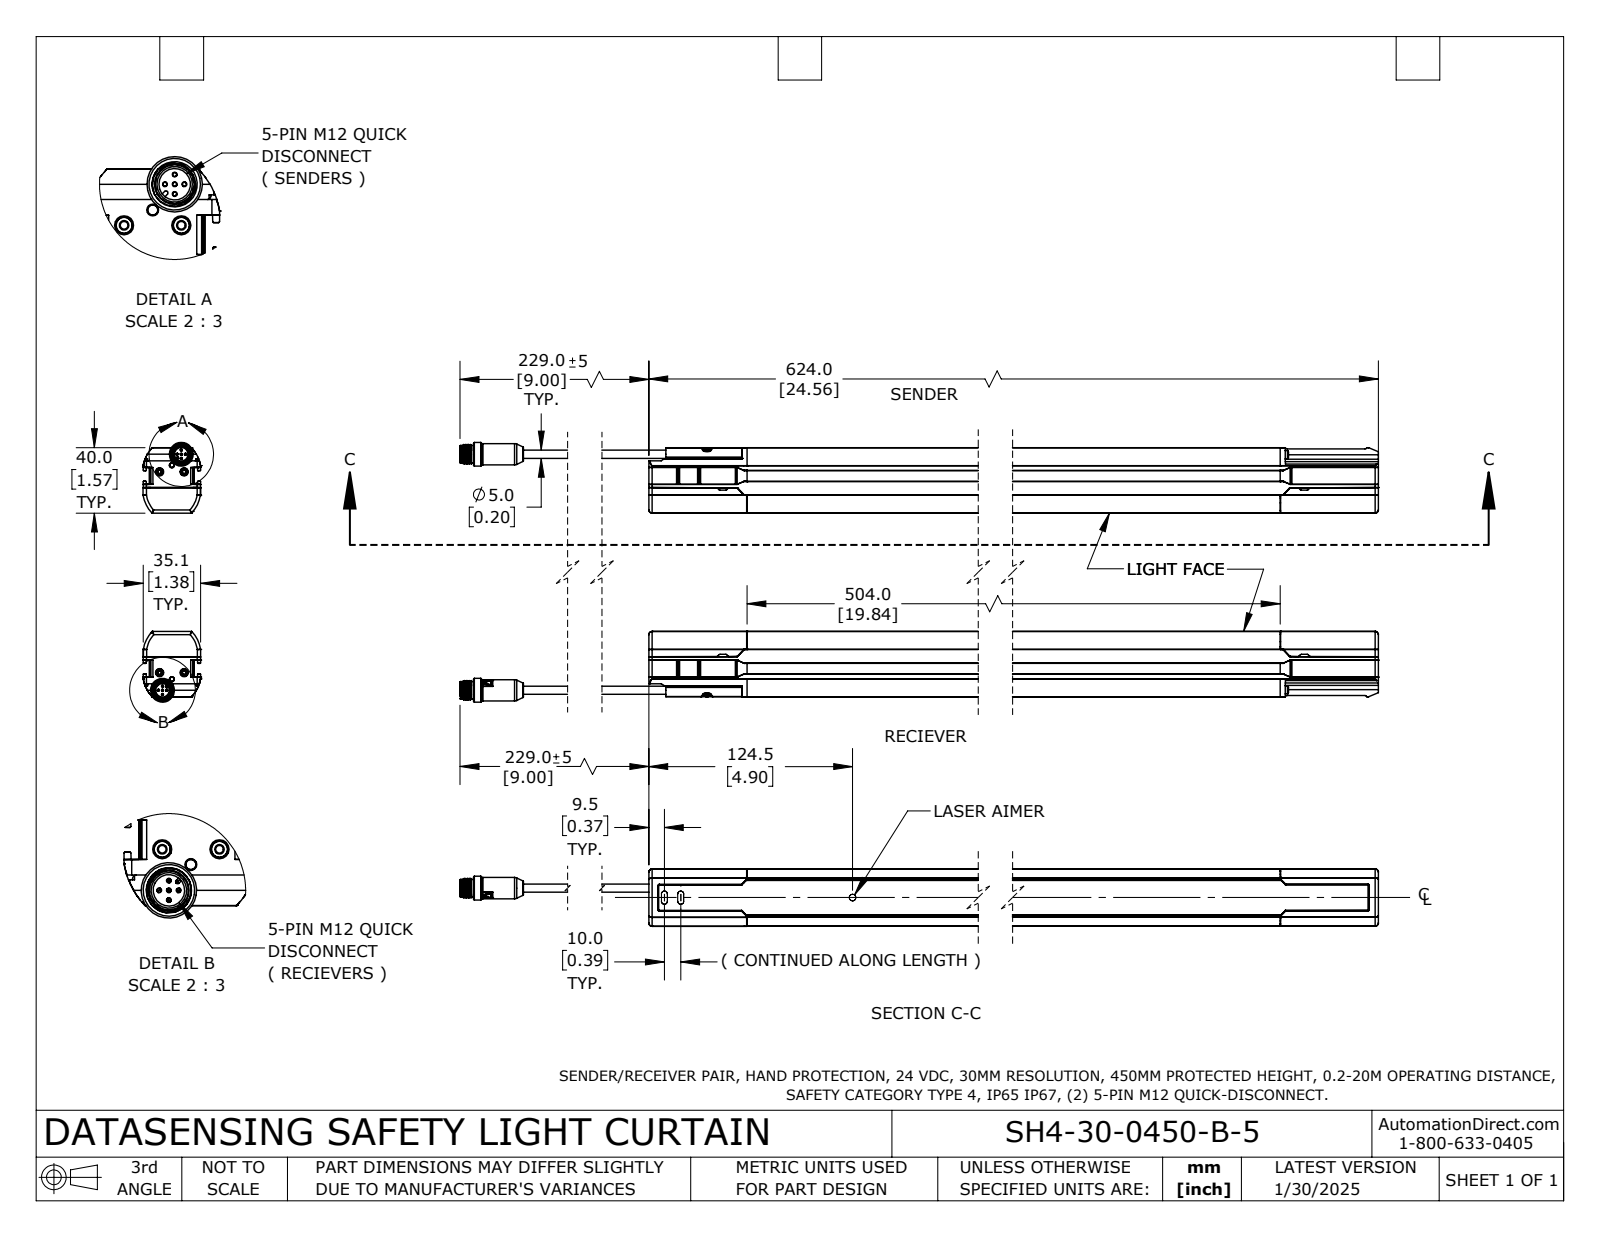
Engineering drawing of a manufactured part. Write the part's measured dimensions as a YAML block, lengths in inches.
part_name: "957920002"
step_written_by: "SolidWorks 2024 (AUTOMOTIVE_DESIGN)"
units: inches
bodies: {solids: 4, faces: 2590, planar: 1186, cylindrical: 778, other: 626}
overall_size: [27.059, 6.248, 1.384]
volume: 64.69
surface_area: 347.6
round_holes:
  - {diameter: 0.079, count: 6}
  - {diameter: 0.118, count: 6}
  - {diameter: 0.197, count: 6}
  - {diameter: 0.102, count: 2}
  - {diameter: 0.102, count: 2}
  - {diameter: 0.102, count: 2}
  - {diameter: 0.103, count: 2}
  - {diameter: 0.11, count: 2}
  - {diameter: 0.325, count: 2}
  - {diameter: 0.382, count: 2}
  - {diameter: 0.407, count: 2}
  - {diameter: 0.425, count: 2}
round_bosses_or_shafts:
  - {diameter: 0.197, count: 10}
  - {diameter: 0.039, count: 10}
  - {diameter: 0.087, count: 8}
  - {diameter: 0.172, count: 6}
  - {diameter: 0.217, count: 4}
  - {diameter: 0.571, count: 2}
  - {diameter: 0.512, count: 2}
  - {diameter: 0.417, count: 2}
partial_cylinders:
  - {radius: 0.01, count: 172}
  - {radius: 0.016, count: 72}
  - {radius: 0.02, count: 50}
  - {radius: 0.008, count: 36}
  - {radius: 0.031, count: 26}
  - {radius: 0.047, count: 16}
  - {radius: 0.079, count: 16}
  - {radius: 0.031, count: 12}
face_to_face_distances: [0.039, 1.496, 4.496, 0.156, 1.222, 3, 1.378, 5.992, 0.079, 0.117]
hole_center_spacings: [4.831, 5.254, 0.591, 0.866, 4.867, 5.535, 0.426, 0.427]
